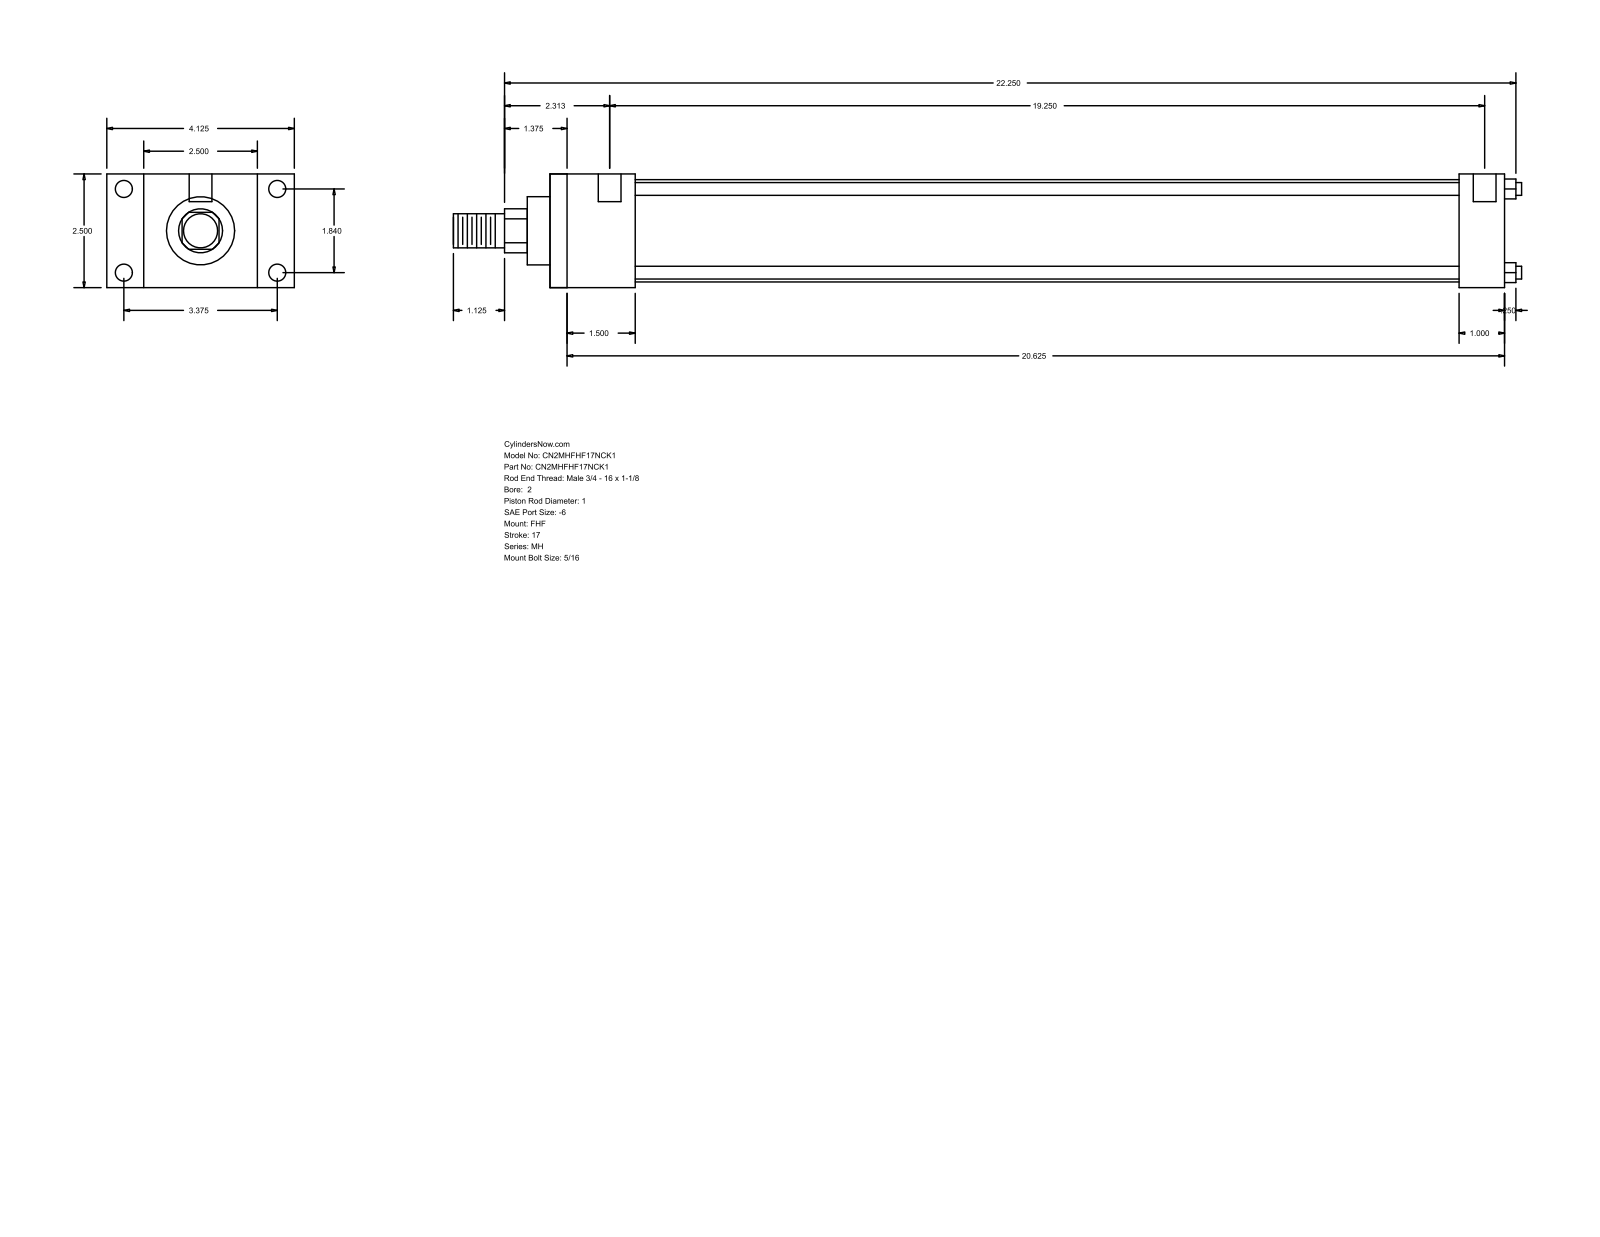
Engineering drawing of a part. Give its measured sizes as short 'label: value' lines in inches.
name: MH_FHF__0200_1
written by: GSSL Pune (CONFIG_CONTROL_DESIGN)
unit: in
bodies: 0 solids, 88 faces (60 planar, 28 cylindrical, 0 other)
size: 23.5 × 4.125 × 2.5
holes: 4× ⌀0.219, 4× ⌀0.375, 2× ⌀0.5
bosses: 4× ⌀0.281, 1× ⌀2.25, 1× ⌀1.5, 1× ⌀1, 1× ⌀0.75
rounds: 1× R0.484
face distances: 2.5, 21, 1.875, 19.125, 0.813, 3.313, 4.125, 1, 20, 18.125
hole spacings: 1.84, 3.375, 3.844, 19.562, 0.125, 0.187, 19.25, 19.375
